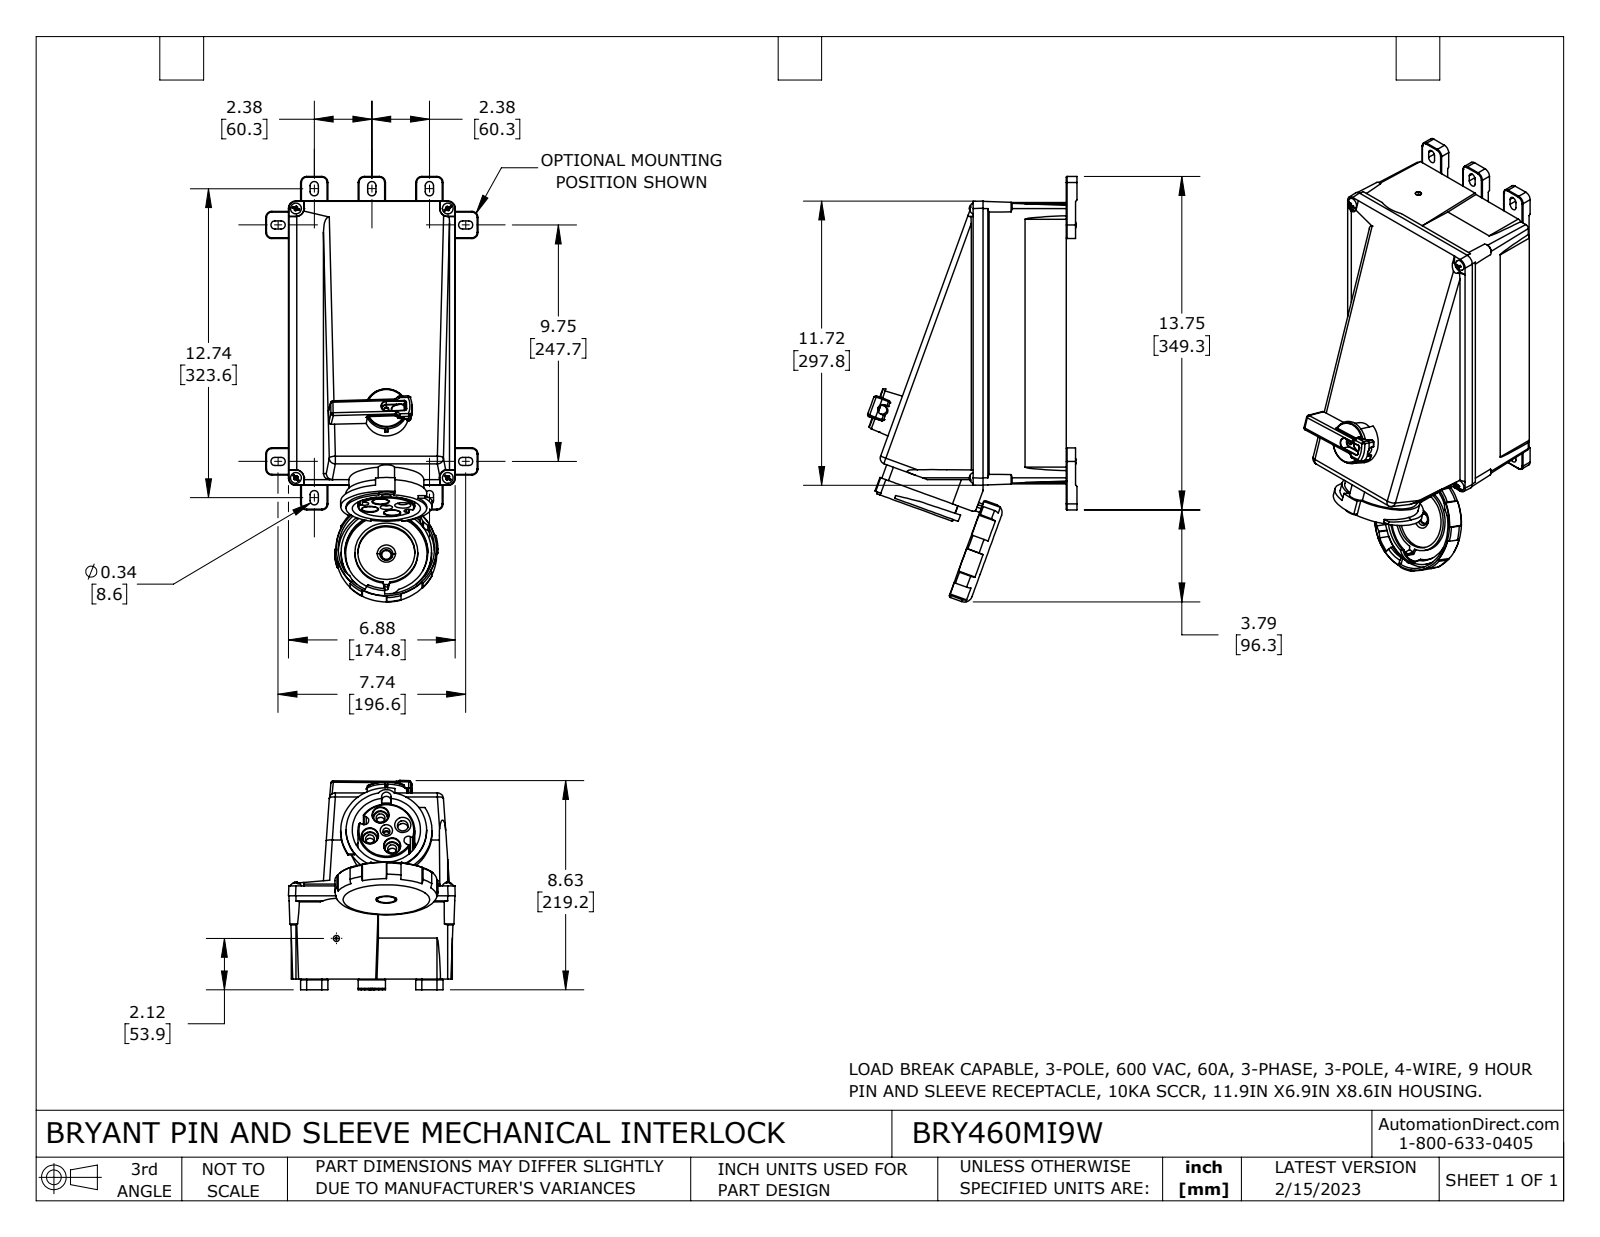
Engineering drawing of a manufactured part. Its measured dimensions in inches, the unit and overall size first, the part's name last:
Units: inches
Overall size (bounding box): 17.549 × 8.635 × 6.88
Round holes (diameter × count): ⌀0.281 ×5, ⌀0.12 ×3, ⌀0.366 ×3, ⌀0.101 ×2, ⌀0.125 ×2, ⌀0.157 ×2, ⌀0.25 ×2, ⌀0.169 ×1, ⌀0.19 ×1, ⌀0.27 ×1, ⌀0.28 ×1, ⌀0.445 ×1
Round bosses / shafts (diameter × count): ⌀0.433 ×5, ⌀0.263 ×2, ⌀3.73 ×1, ⌀3.323 ×1, ⌀3.091 ×1, ⌀2.592 ×1, ⌀2.342 ×1, ⌀0.8 ×1
Partial cylindrical surfaces — rounded edges, fillets, slot ends (radius × count): R0.015 ×135, R0.03 ×41, R0.08 ×30, R0.02 ×24, R0.09 ×19, R0.25 ×16, R0.075 ×12, R0.17 ×10
Main face-to-face distances: 3.44, 6.646, 11.594, 5.528, 0.14, 5.388, 0.15, 6.818, 5.363, 0.025
Hole centre spacings: 0.71, 1.595, 1.016, 1.42, 0.59, 0.59, 0.71, 1.595
Volume: 426.5 in³ · Surface area: 821.7 in²
Bodies: 17 solids, 2001 faces (760 planar, 640 cylindrical, 601 other)
Part name (STEP PRODUCT): BRY460MI9W
STEP written by: SolidWorks 2021 (CONFIG_CONTROL_DESIGN)
